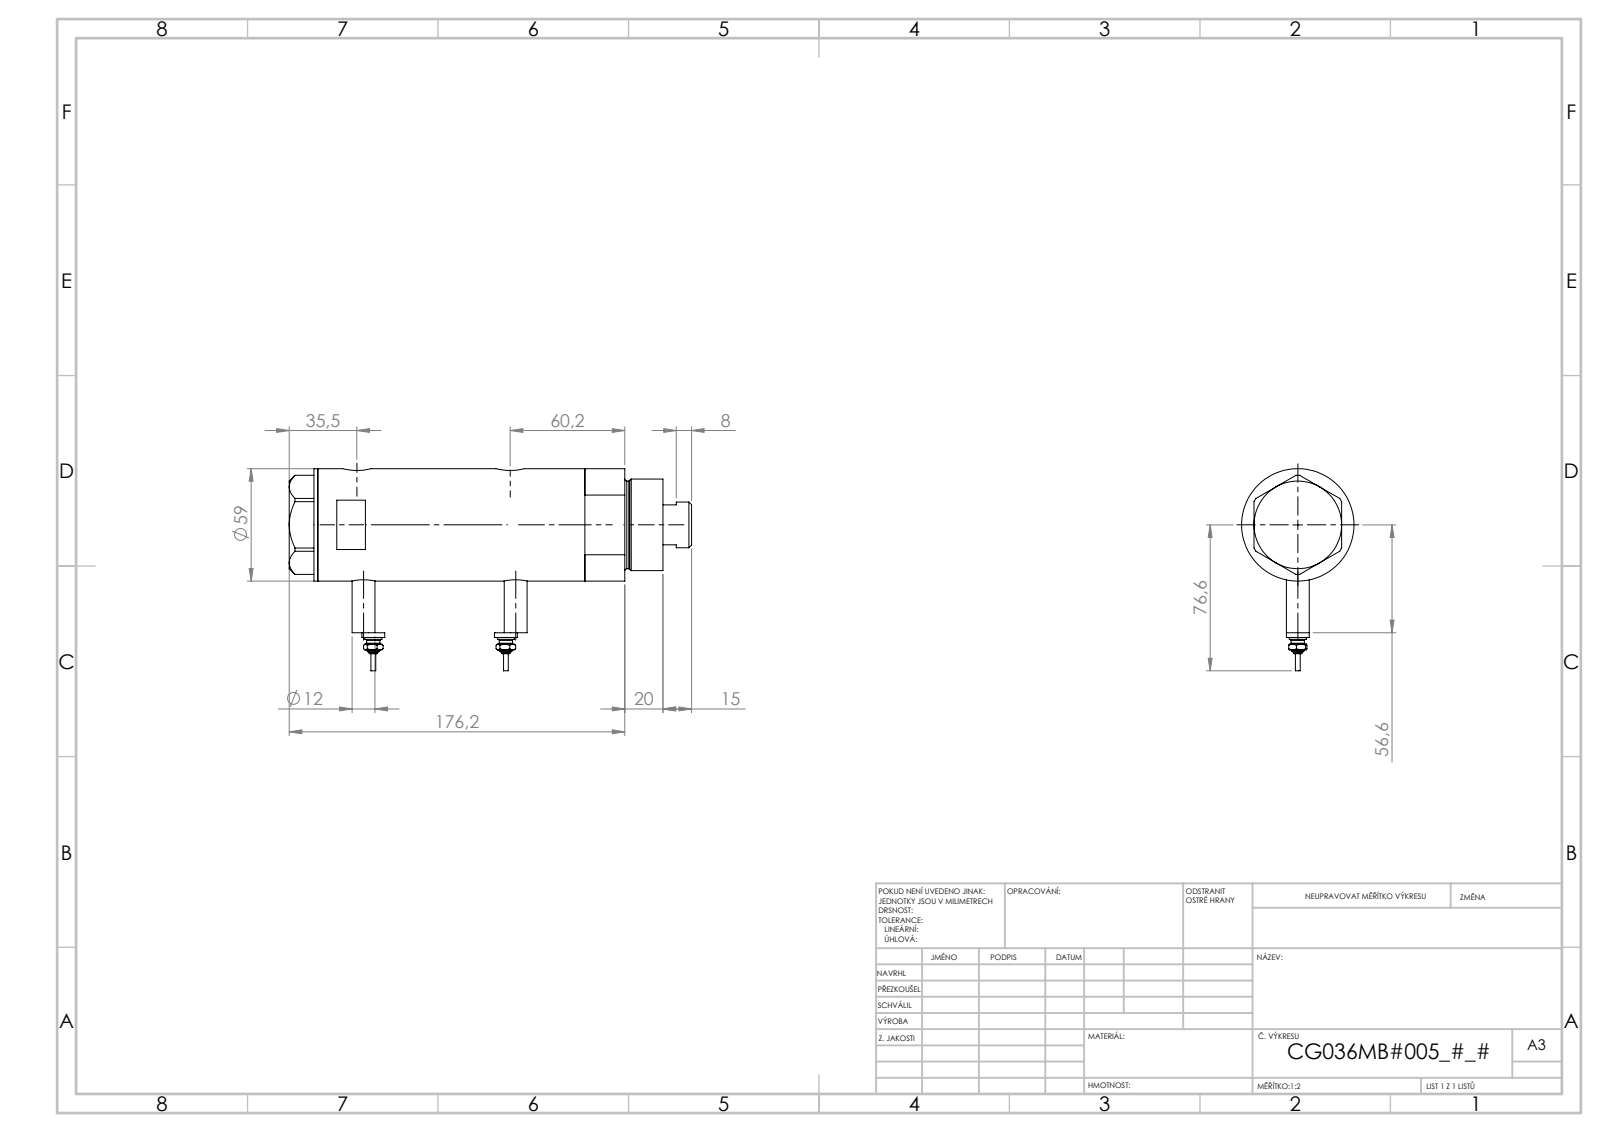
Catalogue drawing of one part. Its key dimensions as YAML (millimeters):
part_name: "V270CG_SWITCH; V270CG_VC; V270CG_MIDDLE; V270CG_BACK (+1 more)"
step_written_by: "SolidWorks 2019 (CONFIG_CONTROL_DESIGN)"
units: millimeters
bodies: {solids: 6, faces: 232, planar: 81, cylindrical: 77, other: 74}
overall_size: [168.42, 91.3, 59]
volume: 385033
surface_area: 85725
round_holes:
  - {diameter: 5, count: 2}
  - {diameter: 9.73, count: 2}
  - {diameter: 12.5, count: 2}
  - {diameter: 15, count: 2}
  - {diameter: 8.5, count: 1}
  - {diameter: 25, count: 1}
  - {diameter: 26.5, count: 1}
  - {diameter: 36, count: 1}
  - {diameter: 40, count: 1}
  - {diameter: 52, count: 1}
round_bosses_or_shafts:
  - {diameter: 12, count: 3}
  - {diameter: 9, count: 2}
  - {diameter: 7, count: 2}
  - {diameter: 4.34, count: 2}
  - {diameter: 2.4, count: 2}
  - {diameter: 59, count: 1}
  - {diameter: 48, count: 1}
  - {diameter: 46, count: 1}
face_to_face_distances: [62.34, 23.5, 38.84, 15, 38.5, 77.34, 153.42, 138.42, 114.92, 76.08]
hole_center_spacings: [2.9, 3.5, 37.15, 40.05, 40.65, 43.55, 2.89, 2.91]
